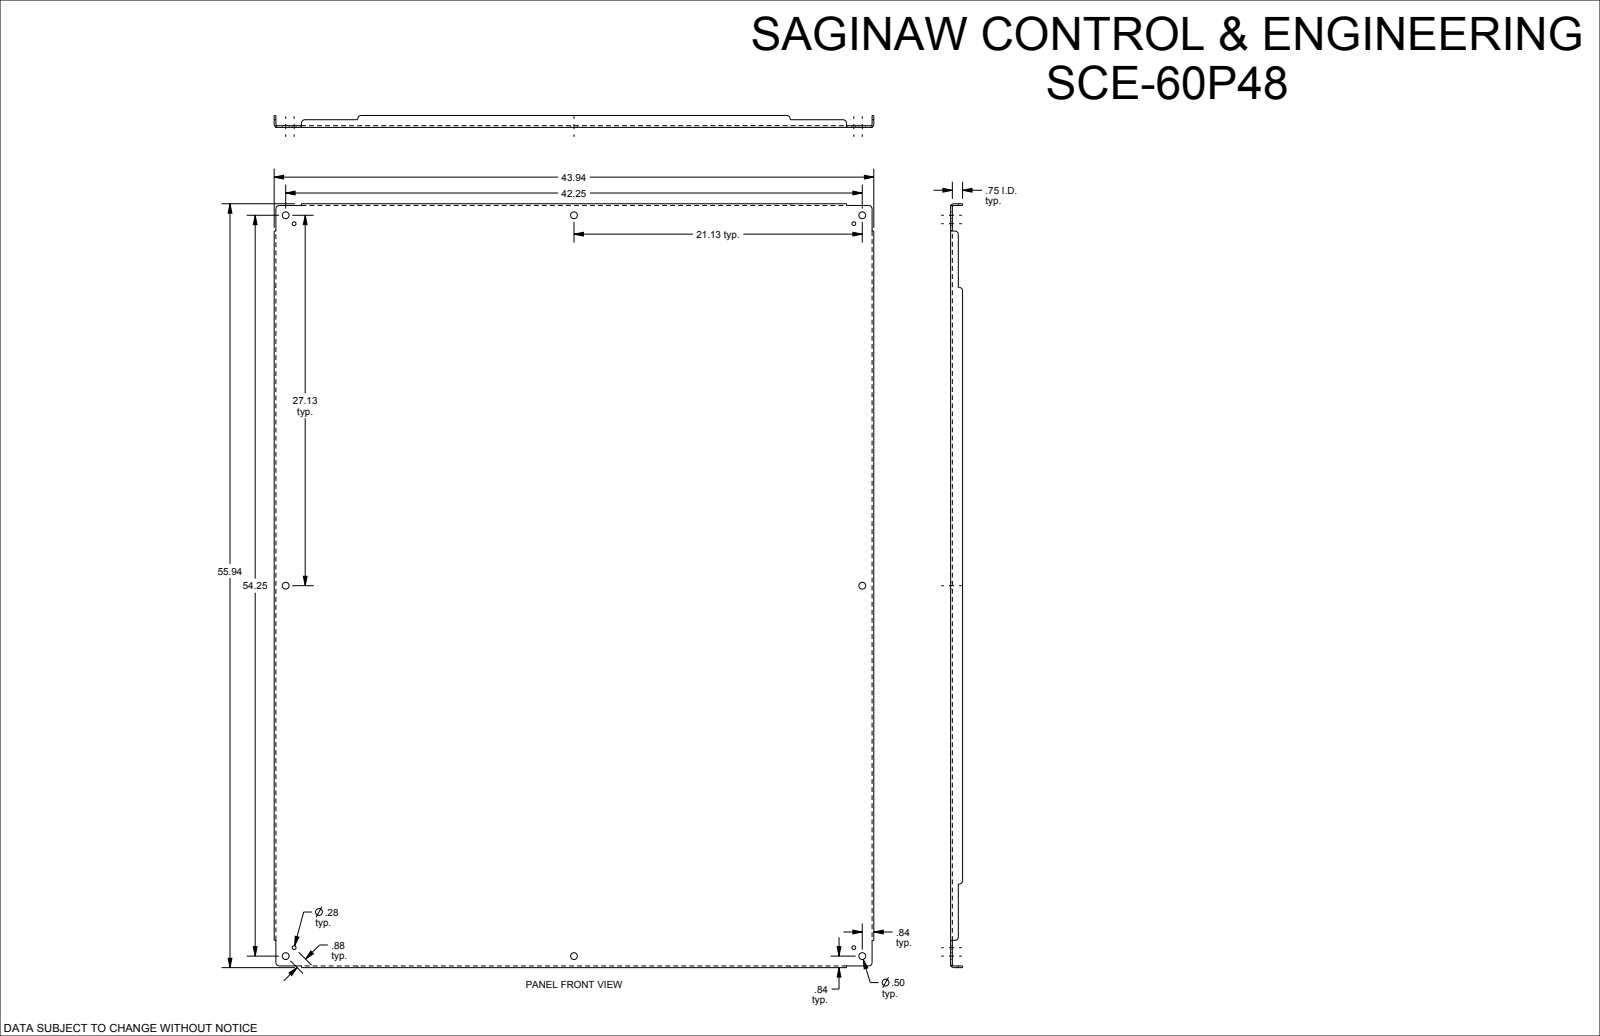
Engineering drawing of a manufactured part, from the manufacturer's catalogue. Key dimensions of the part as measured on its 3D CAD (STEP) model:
Part name (STEP PRODUCT): SCE-60P48
STEP written by: SolidWorks 2019 (CONFIG_CONTROL_DESIGN)
Units: inches
Bodies: 1 solid, 110 faces (46 planar, 40 cylindrical, 24 other)
Overall size (bounding box): 55.938 × 43.938 × 0.875
Volume: 320.9 in³ · Surface area: 5 162 in²
Round holes (diameter × count): ⌀0.5 ×8, ⌀0.281 ×4
Partial cylindrical surfaces — rounded edges, fillets, slot ends (radius × count): R0.25 ×12, R0.112 ×4, R0.237 ×4
Main face-to-face distances: 0.125, 0.125, 43.813, 55.813, 43.687, 43.938, 55.687, 55.938, 0.75, 0.875
Hole centre spacings: 0.875, 20.516, 21.125, 26.513, 27.125, 34.38, 41.636, 49.353
